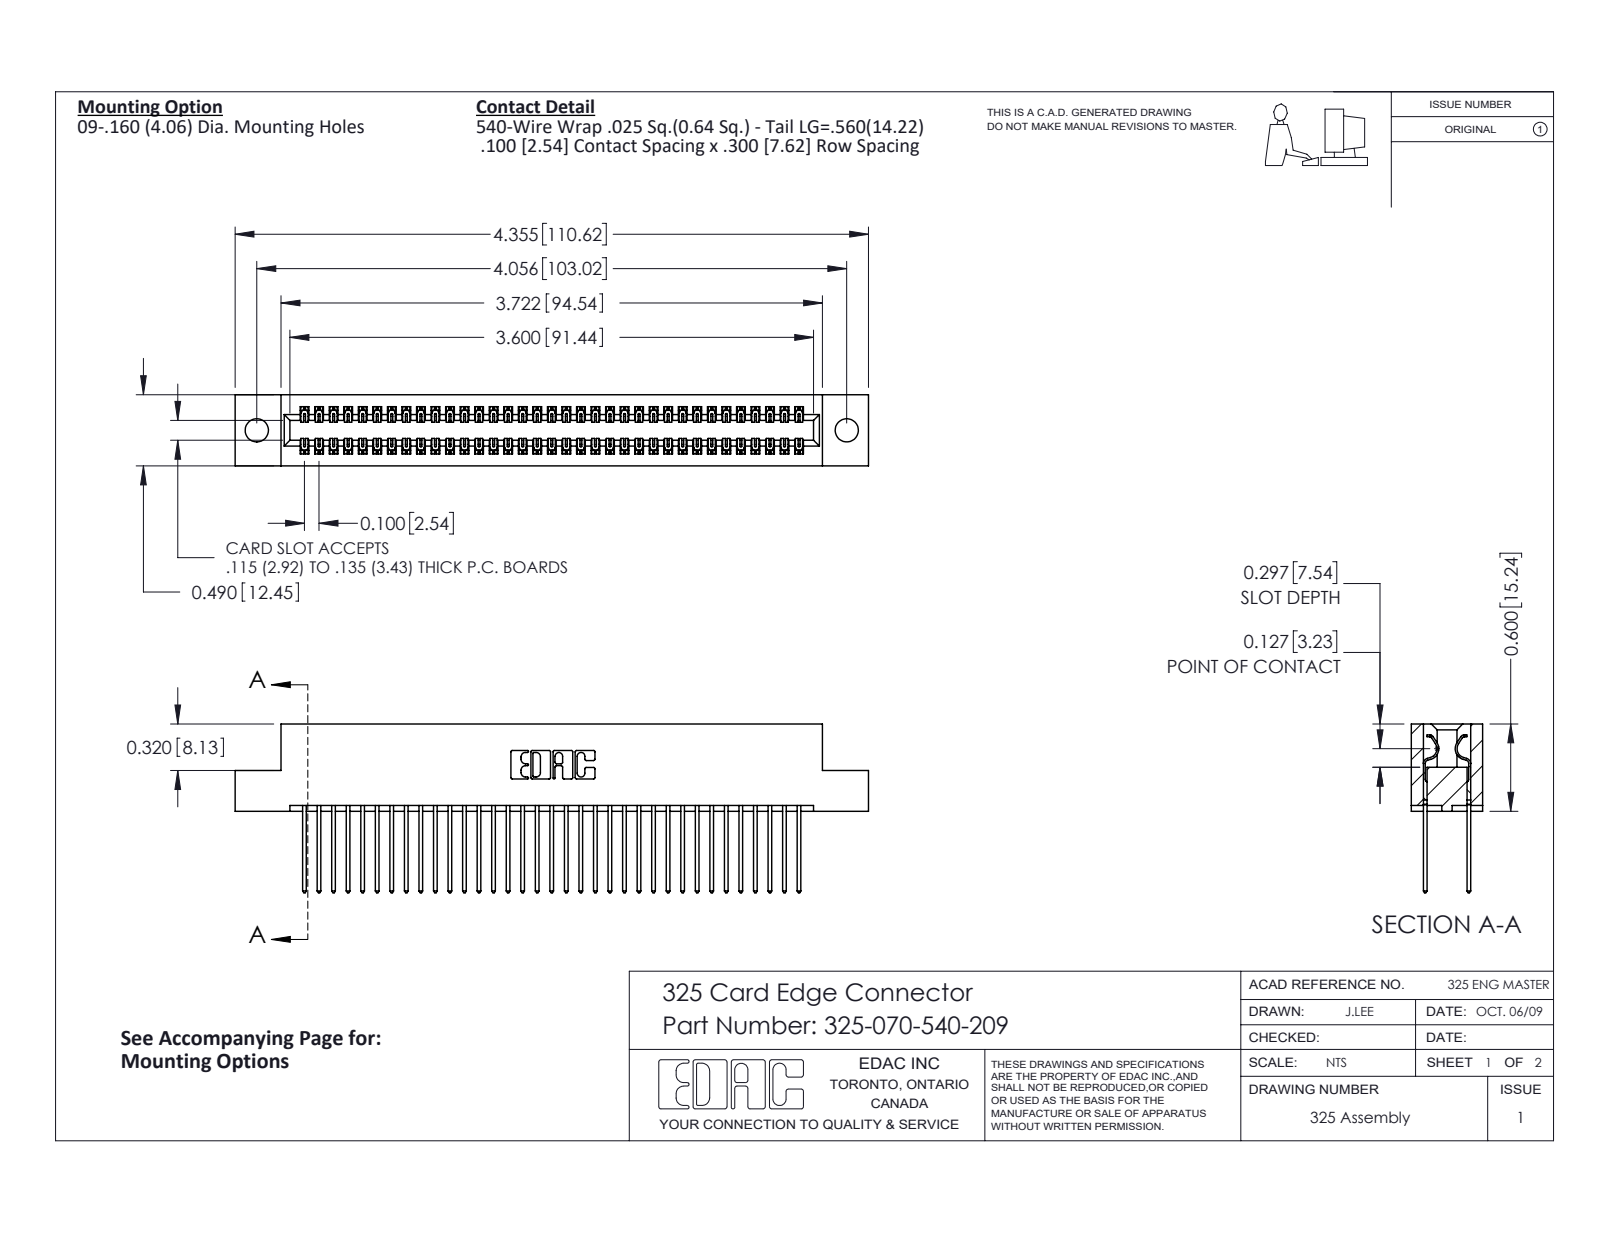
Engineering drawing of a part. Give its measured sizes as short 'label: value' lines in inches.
name: 325 Part_.160 TH; 325-292-001_325-293-140; 325-070-540-209
written by: SolidWorks 2016 (CONFIG_CONTROL_DESIGN)
unit: in
bodies: 71 solids, 3754 faces (2590 planar, 1164 cylindrical, 0 other)
size: 4.355 × 1.16 × 0.49
volume: 0.87 in³; area: 28.32 in²
holes: 2× ⌀0.16
rounds: 105× R0.006, 70× R0.01, 22× R0.01, 6× R0.007, 6× R0.031, 3× R0.026, 2× R0.014, 2× R0.022
face distances: 0.083, 0.407, 0.3, 0.107, 0.383, 0.025, 0.49, 0.325, 0.275, 0.56
hole spacings: 4.056
